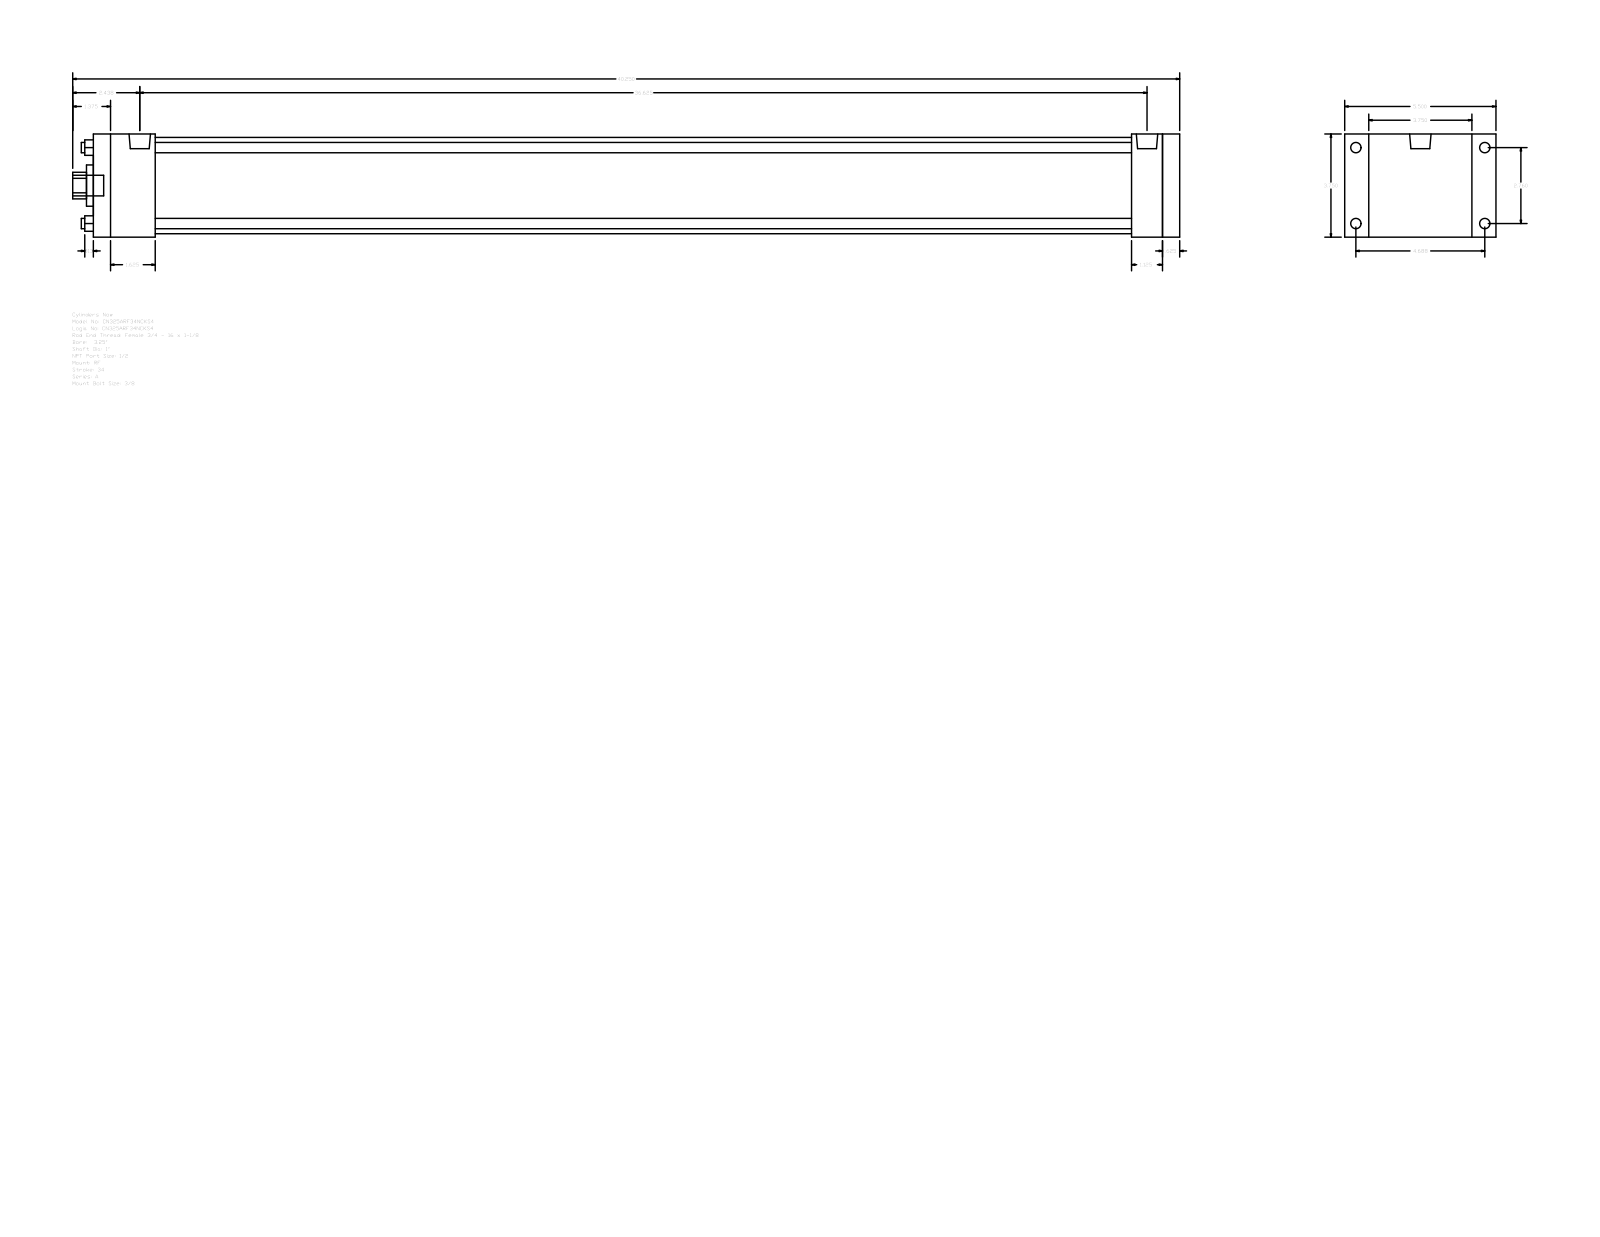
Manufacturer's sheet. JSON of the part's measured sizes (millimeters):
{"part_name": "A_RF__0325_1", "step_written_by": "GSSL Pune (CONFIG_CONTROL_DESIGN)", "units": "millimeters", "bodies": {"solids": 0, "faces": 92, "planar": 64, "cylindrical": 28, "other": 0}, "overall_size": [1022.35, 139.7, 95.25], "round_holes": [[9.53, 4], [25.4, 1], [38.1, 1], [88.9, 1]], "round_bosses_or_shafts": [[9.53, 4], [8.73, 4], [19.77, 2], [19.05, 1]], "partial_cylinders_radius": [[12.29, 1]], "face_to_face_distances": [95.24, 1003.3, 15.87, 987.43, 22.23, 117.47, 958.85, 28.58, 44.45, 57.15], "hole_center_spacings": [49.57, 70.1, 99.14]}
